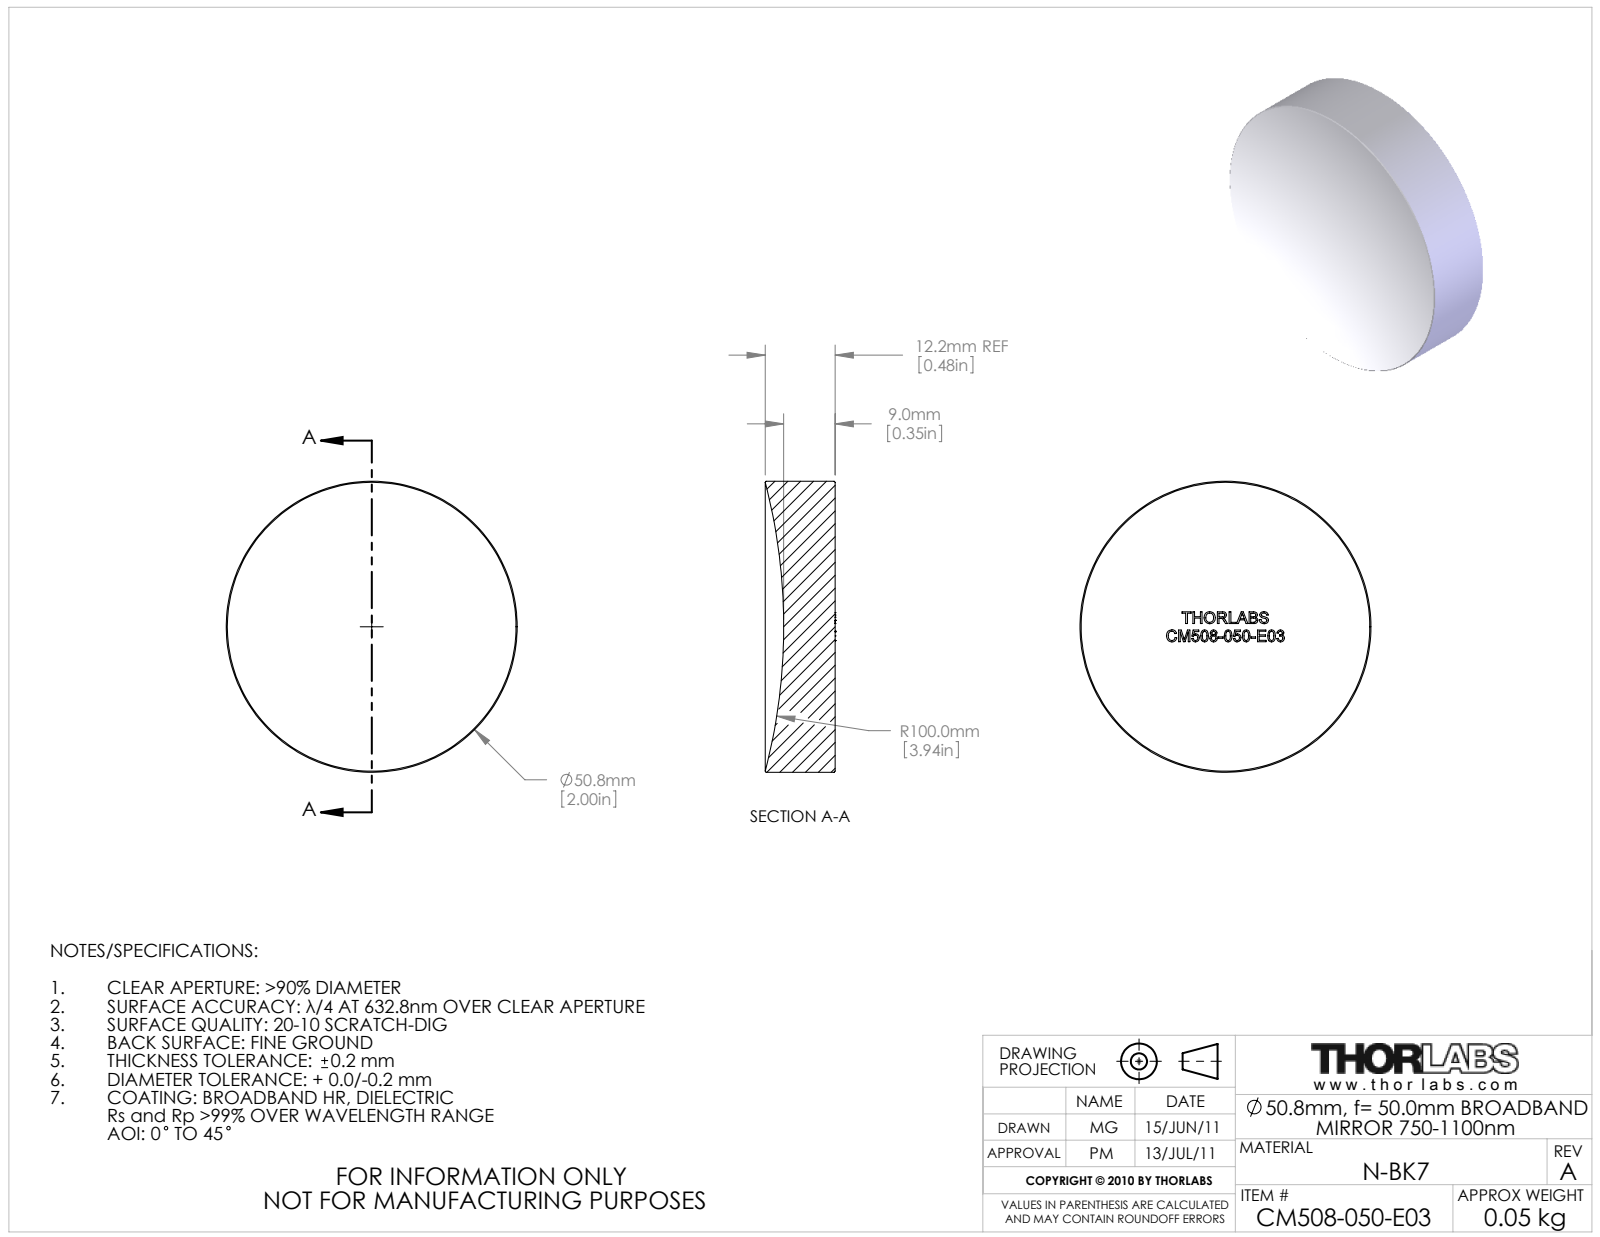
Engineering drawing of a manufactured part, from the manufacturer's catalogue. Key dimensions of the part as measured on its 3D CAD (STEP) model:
Part name (STEP PRODUCT): 22645-E0W
STEP written by: SolidWorks 2011 (AUTOMOTIVE_DESIGN)
Units: millimetres
Bodies: 0 solids, 43 faces (35 planar, 2 cylindrical, 6 other)
Overall size (bounding box): 50.8 × 50.8 × 12.23
Round bosses / shafts (diameter × count): ⌀50.8 ×1
Main face-to-face distances: 2.05
